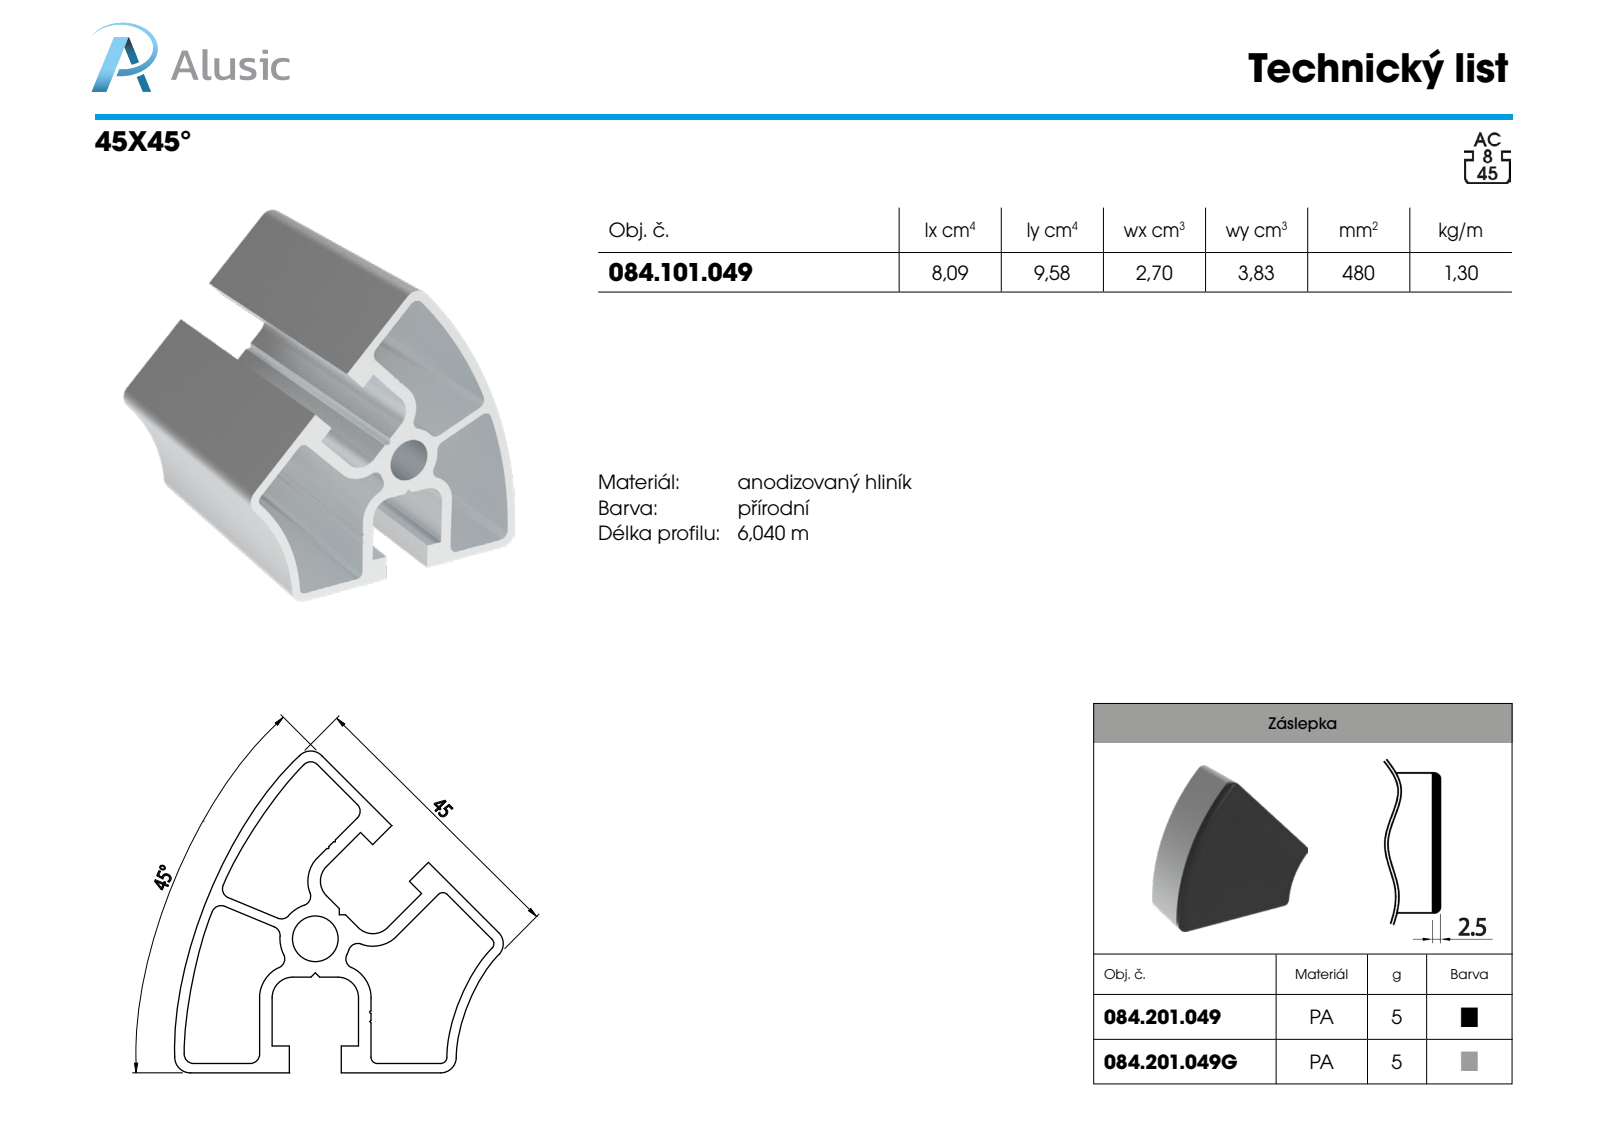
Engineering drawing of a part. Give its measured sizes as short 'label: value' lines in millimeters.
name: 084.201.049
written by: SolidWorks 2011 (CONFIG_CONTROL_DESIGN)
unit: mm
bodies: 1 solid, 104 faces (23 planar, 29 cylindrical, 52 other)
size: 52.54 × 51.45 × 12.25
volume: 5 508 mm³; area: 6 417 mm²
holes: 4× ⌀9.5
bosses: 4× ⌀11
rounds: 4× R2.5, 2× R2, 1× R3.65, 1× R27, 1× R72
face distances: 2.5, 1.2, 0.5, 3, 4, 4.5, 7, 4.42
hole spacings: 30.6, 14.07, 37.49, 38.26, 38.27
